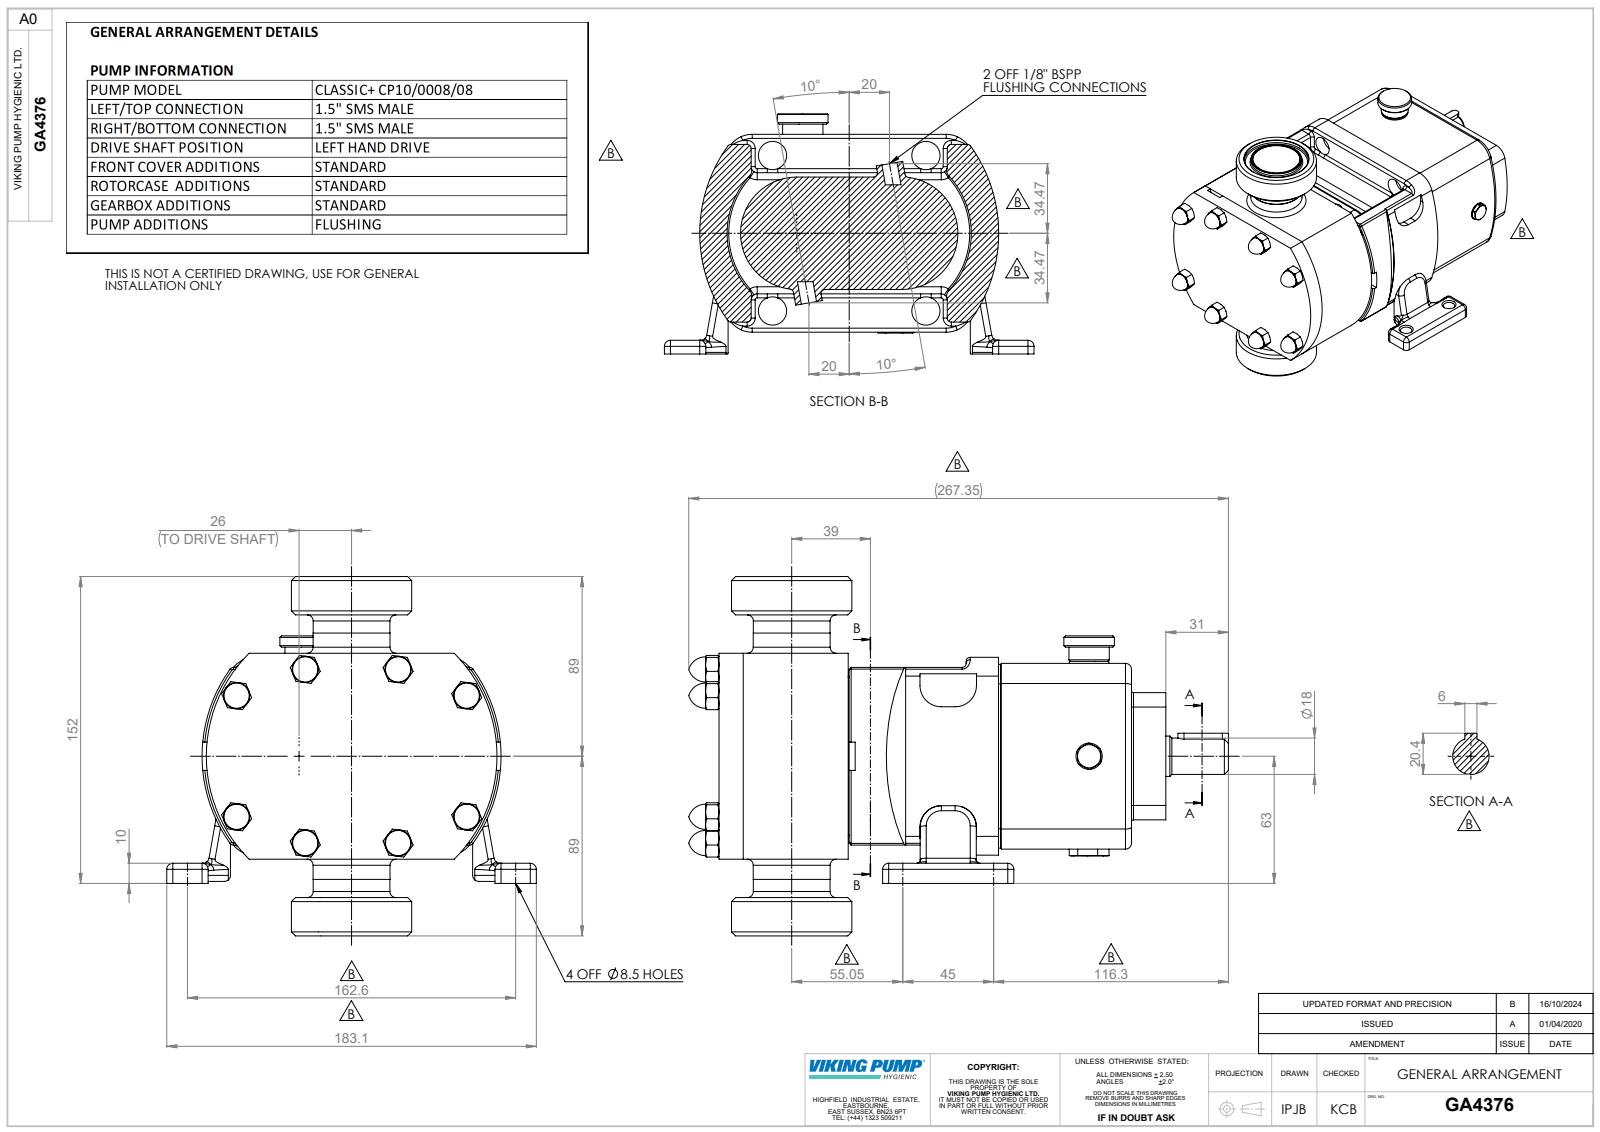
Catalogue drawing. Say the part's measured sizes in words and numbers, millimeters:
The part is named "Copy of Z94-5101-22 - 1.5 INCH SMS681^GA4376; GA4376; Copy of CP10-0008-08 V L^GA4376". Its 3-D file was written by "SolidWorks 2023 (AUTOMOTIVE_DESIGN)". It is 3 solids with 798 faces: 254 planar, 224 cylindrical and 320 other. Overall it measures 267.35 by 183.1 by 178 millimeters. Its volume is 2 517 000 cubic millimeters and its surface area 195 580 square millimeters. Round holes: 4 of diameter 8.5, 4 of diameter 14, 2 of diameter 7.63, 1 of diameter 22.53, 1 of diameter 35, 1 of diameter 48. Round bosses or shafts: 2 of diameter 30, 1 of diameter 59.6, 1 of diameter 38.1, 1 of diameter 38, 1 of diameter 37.6, 1 of diameter 25.02, 1 of diameter 19.99, 1 of diameter 19.98. Partial cylindrical surfaces (rounded edges, fillets, slot ends): 32 of radius 2, 32 of radius 3, 12 of radius 13.5, 6 of radius 3.5, 6 of radius 10.5, 4 of radius 5.5, 4 of radius 6, 4 of radius 9. The main face-to-face distances are 102, 221.35, 19, 92, 21, 4.99, 97.01, 96.99, 5.01, 124. The hole center spacings are 45, 76, 77.02, 98.18, 108.2, 128.92, 162.6, 168.71.
